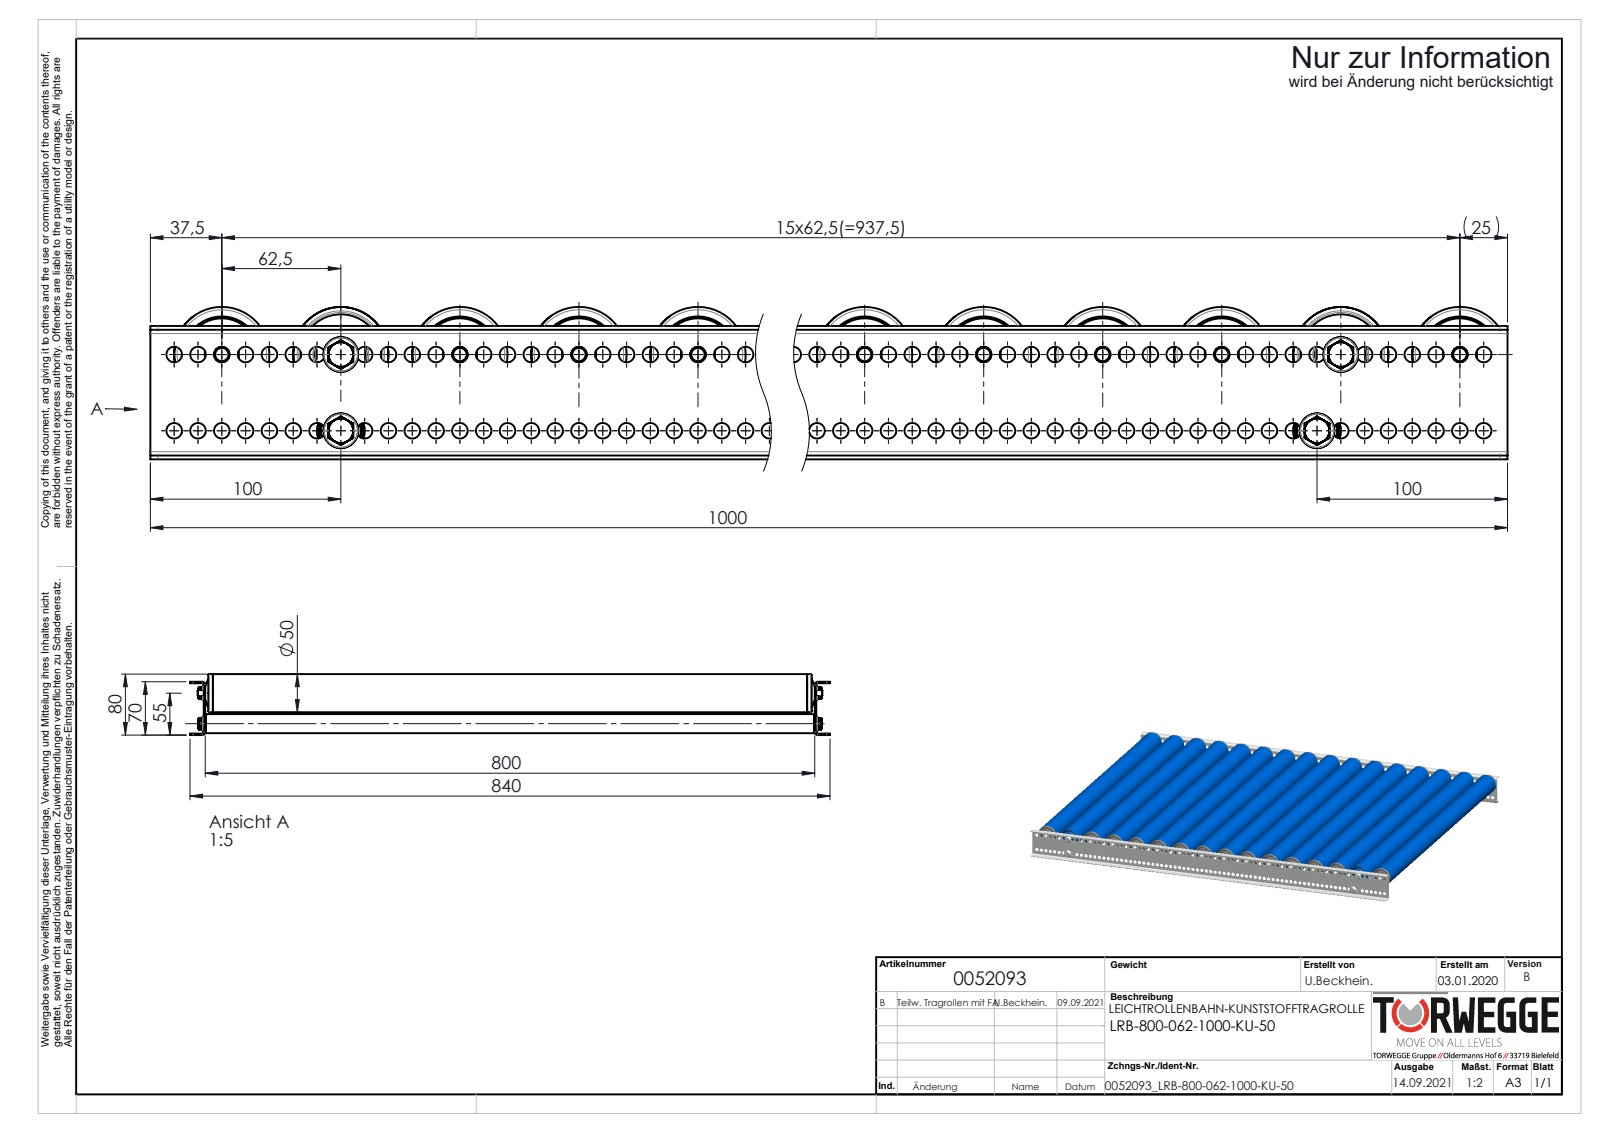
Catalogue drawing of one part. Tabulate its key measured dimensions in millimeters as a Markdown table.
| quantity | value |
| --- | --- |
| part name | 0024178_Passscheibe_DIN988_12x18x1; 0017015_Tragrollenrohr-Ø50x2,8KU_KFG_0017015_L=785; KUT100-50x2,8-KB-A12-IGM8-EL=KFG_S100915_KUT100-50x2,8-KB-A12-IGM8-EL=800; 0039778-Achse-ST-Ø08-KFG_AL820-G (+8 more) |
| STEP written by | SolidWorks 2020 (AUTOMOTIVE_DESIGN) |
| units | millimeters |
| bodies | 274 solids, 5068 faces (1336 planar, 2192 cylindrical, 1540 other) |
| overall size | 1000 × 840 × 80 |
| volume | 7 444 000 mm³ |
| surface area | 5 378 000 mm² |
| round holes (diameter × count) | 8.2 × 158, 7.6 × 14, 8 × 14, 25 × 14, 30 × 14, 35 × 14, 39.4 × 14, 40 × 14, 6.8 × 4, 12 × 2, 12.1 × 2, 16 × 2 |
| round bosses / shafts (diameter × count) | 50 × 16, 44.4 × 14, 38 × 14, 36 × 14, 33 × 14, 22 × 14, 21 × 14, 25 × 4 |
| partial cylindrical surfaces (radius × count) | 0.6 × 28, 0.75 × 28, 2.45 × 28, 4.87 × 14, 7 × 14, 4 × 8, 2 × 4, 2.5 × 4 |
| main face-to-face distances | 2, 802, 68, 800, 804, 792, 66, 70, 12, 6 |
| hole center spacings | 12.5, 25, 37.5, 50, 62.5, 75, 87.5, 100 |
